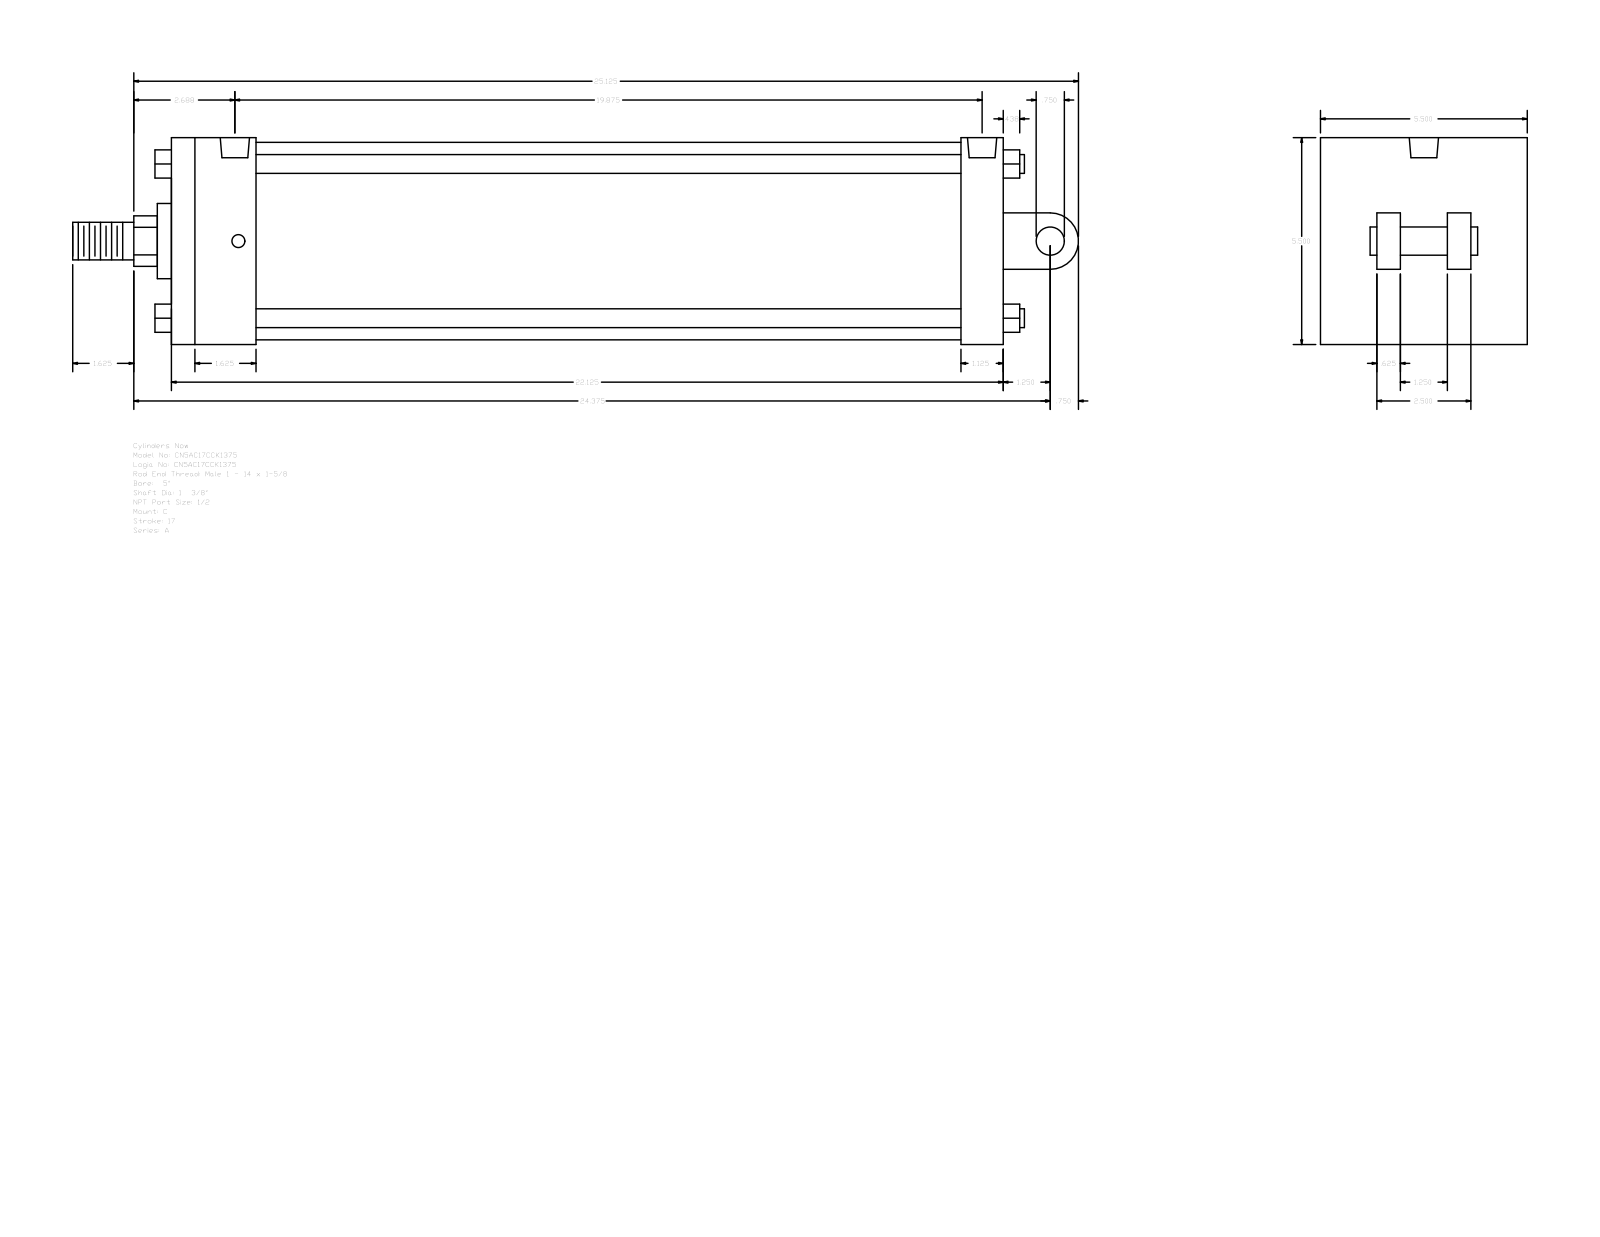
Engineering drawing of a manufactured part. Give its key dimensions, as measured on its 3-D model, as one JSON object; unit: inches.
{"part_name": "A_C__0500_1.375", "step_written_by": "GSSL Pune (CONFIG_CONTROL_DESIGN)", "units": "inches", "bodies": {"solids": 0, "faces": 135, "planar": 102, "cylindrical": 33, "other": 0}, "overall_size": [26.75, 5.5, 5.5], "round_holes": [[0.344, 4], [0.778, 2]], "round_bosses_or_shafts": [[0.5, 4], [5.25, 1], [2, 1], [1.375, 1], [1, 1], [0.75, 1]], "partial_cylinders_radius": [[0.672, 1], [0.75, 1]], "face_to_face_distances": [5.5, 22.125, 2.25, 1.125, 21, 18.75, 19.875, 1.5, 2.125, 3.375], "hole_center_spacings": [0.094, 19.687, 19.781, 19.875]}
